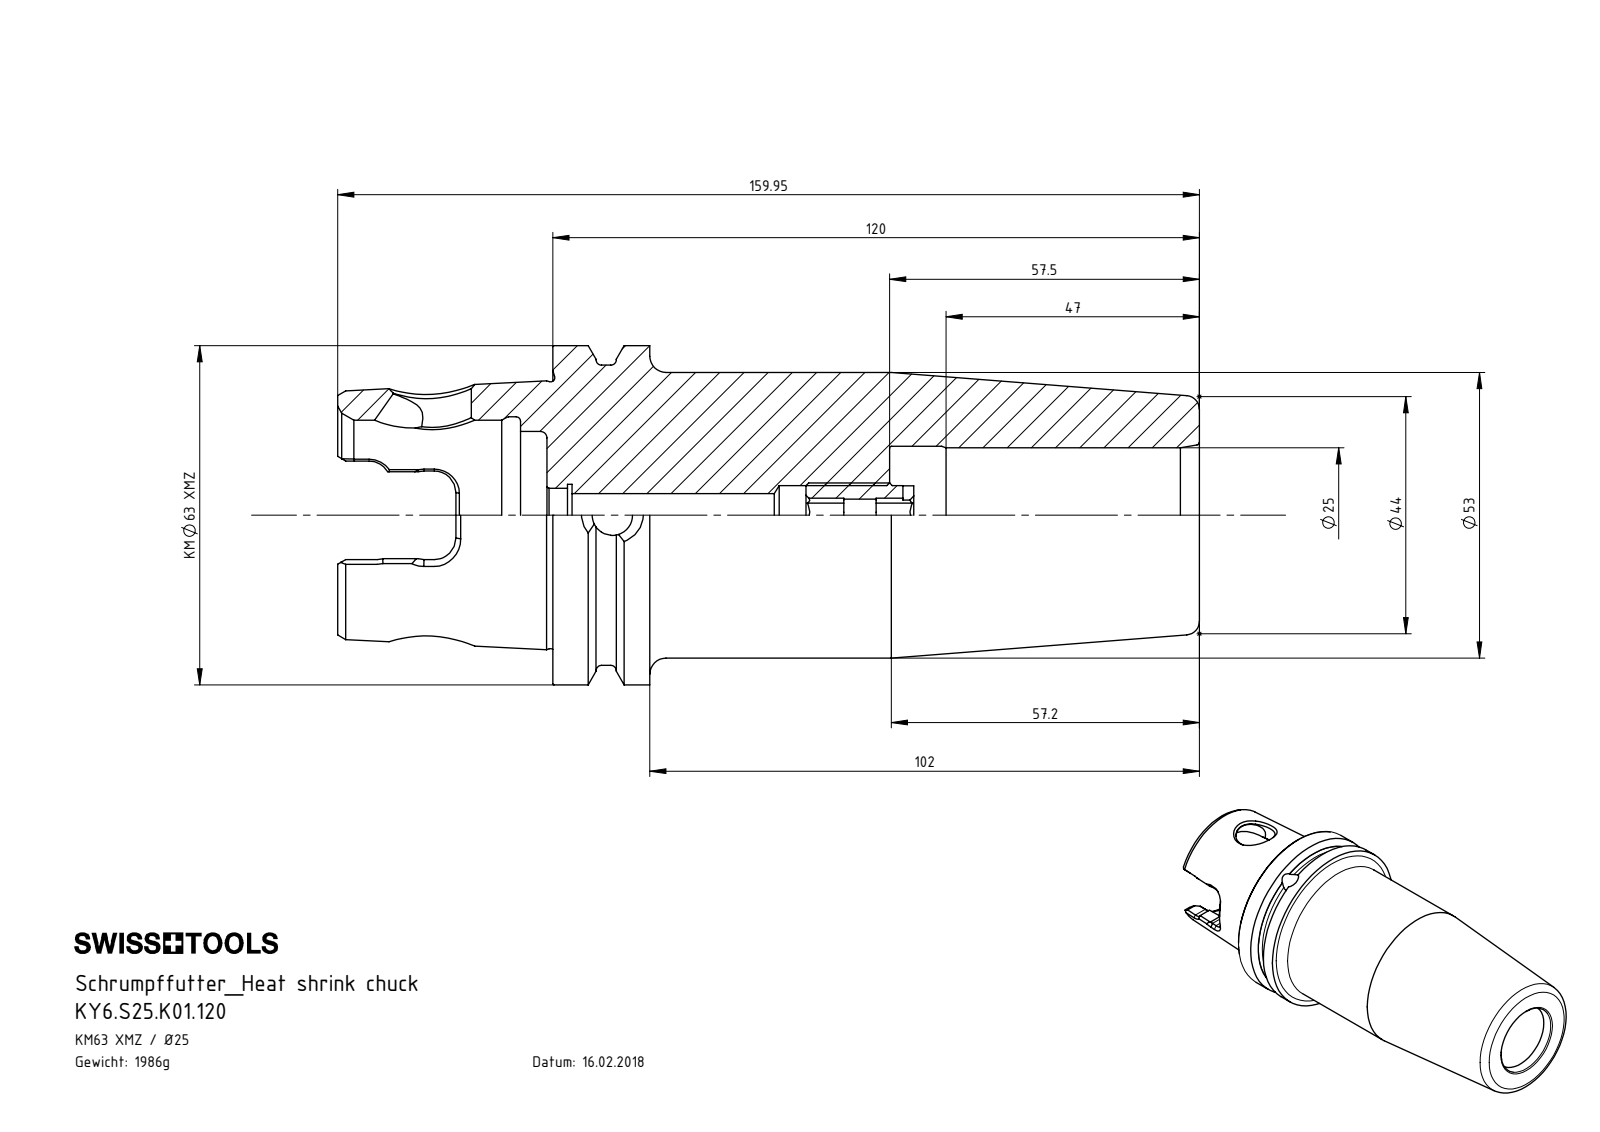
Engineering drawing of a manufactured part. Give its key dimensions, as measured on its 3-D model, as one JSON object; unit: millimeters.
{"part_name": "KY6.S25.K01.120; ERU-AN5.K01.020_A; KY6-S25.K01.120_A", "step_written_by": "SolidWorks 2017 (CONFIG_CONTROL_DESIGN)", "units": "millimeters", "bodies": {"solids": 2, "faces": 277, "planar": 79, "cylindrical": 60, "other": 138}, "overall_size": [159.95, 62.95, 62.95], "volume_mm3": 253000, "surface_area_mm2": 42400, "round_holes": [[7.47, 2], [6, 1], [8, 1], [8.48, 1], [10, 1], [11, 1], [11.5, 1], [14.5, 1], [25, 1], [25.6, 1], [31.1, 1], [35.27, 1]], "round_bosses_or_shafts": [[62.95, 1], [55.7, 1], [53, 1], [12, 1]], "partial_cylinders_radius": [[4, 6], [7.04, 2]], "face_to_face_distances": [120, 1.1, 121.1, 18, 19.1, 102, 63.6, 62.5, 44.5, 57.5]}
